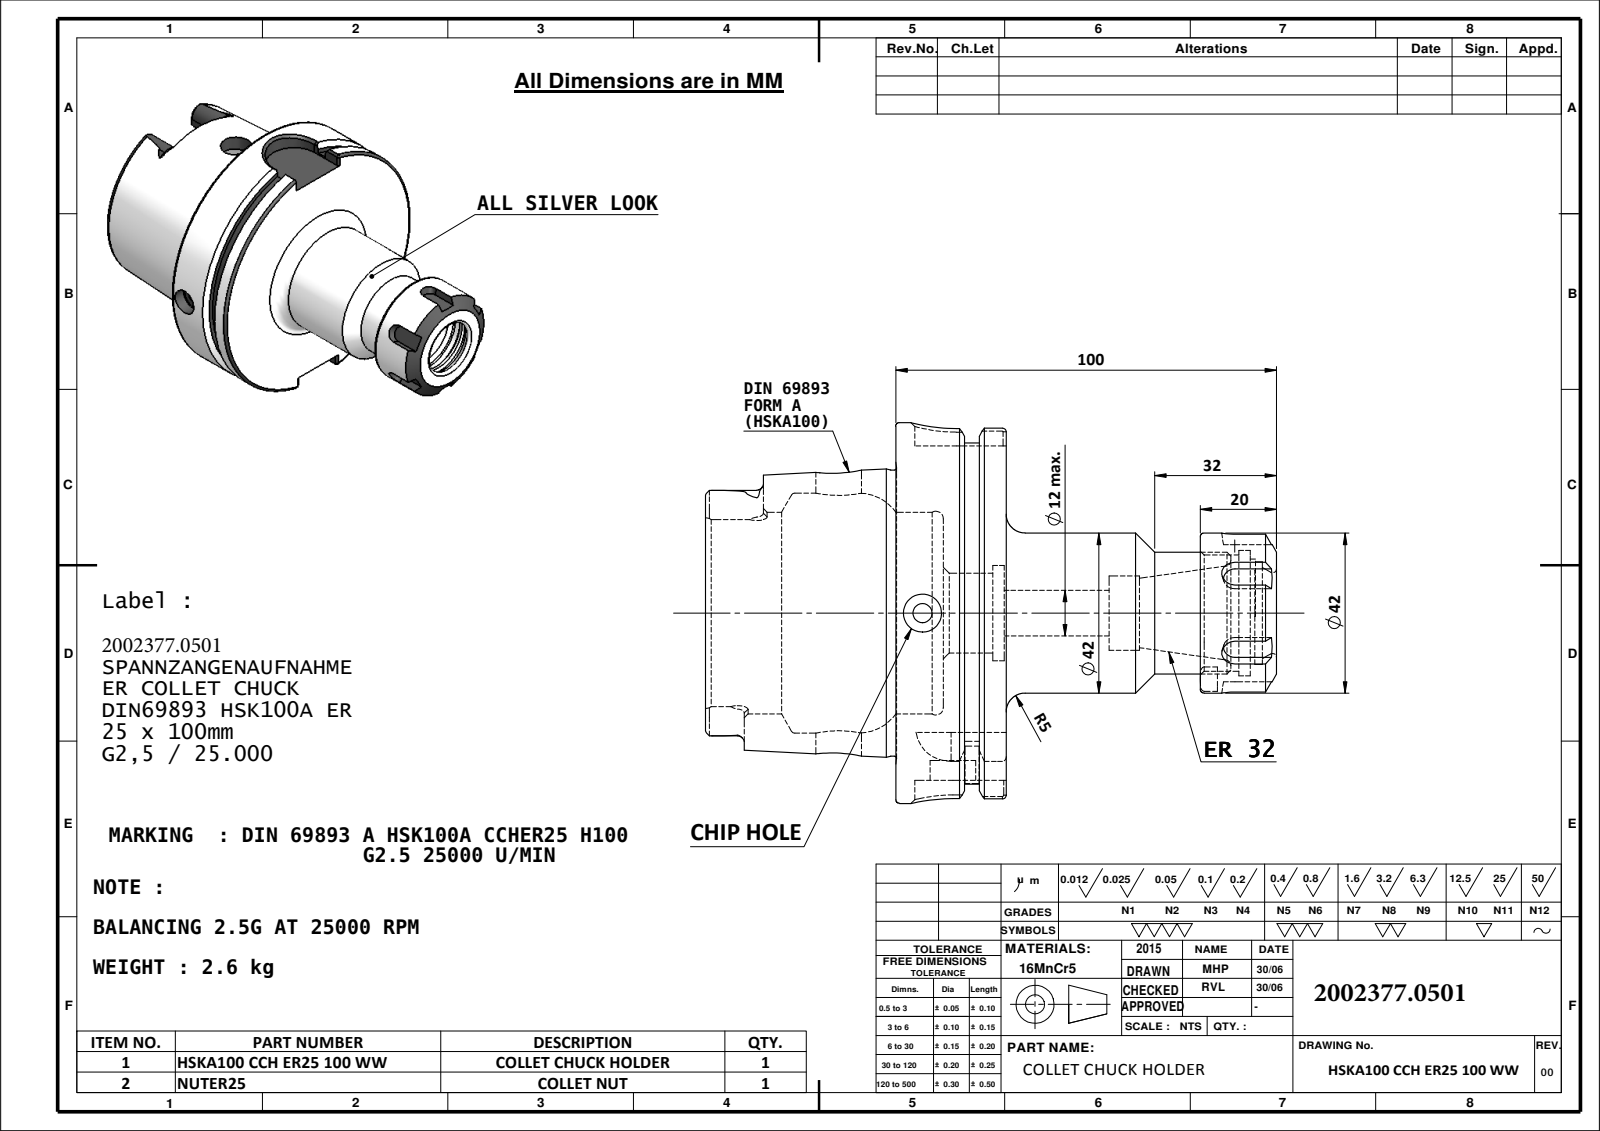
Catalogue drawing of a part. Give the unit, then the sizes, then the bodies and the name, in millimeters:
Units: millimetres
Overall size (bounding box): 150 × 100 × 100
Round holes (diameter × count): ⌀12 ×3, ⌀10 ×1, ⌀19.5 ×1, ⌀21 ×1, ⌀25 ×1, ⌀25.8 ×1, ⌀27 ×1, ⌀30.5 ×1, ⌀33 ×1, ⌀53 ×1, ⌀63 ×1
Round bosses / shafts (diameter × count): ⌀100 ×1, ⌀92 ×1, ⌀75.16 ×1, ⌀42 ×1, ⌀32 ×1
Partial cylindrical surfaces — rounded edges, fillets, slot ends (radius × count): R1.8 ×6, R4.88 ×4, R10 ×2, R11 ×1
Main face-to-face distances: 29, 12.5, 16.5, 62.5, 50, 79, 20, 64.6, 130, 80
Hole centre spacings: 1.5, 30
Volume: 321 123 mm³ · Surface area: 65 816 mm²
Bodies: 2 solids, 234 faces (81 planar, 62 cylindrical, 91 other)
Part name (STEP PRODUCT): HSKA100 CCH ER25 100 WW; 91100A-ER8 25100; FTNUTER25
STEP written by: SolidWorks 2009 (CONFIG_CONTROL_DESIGN)
